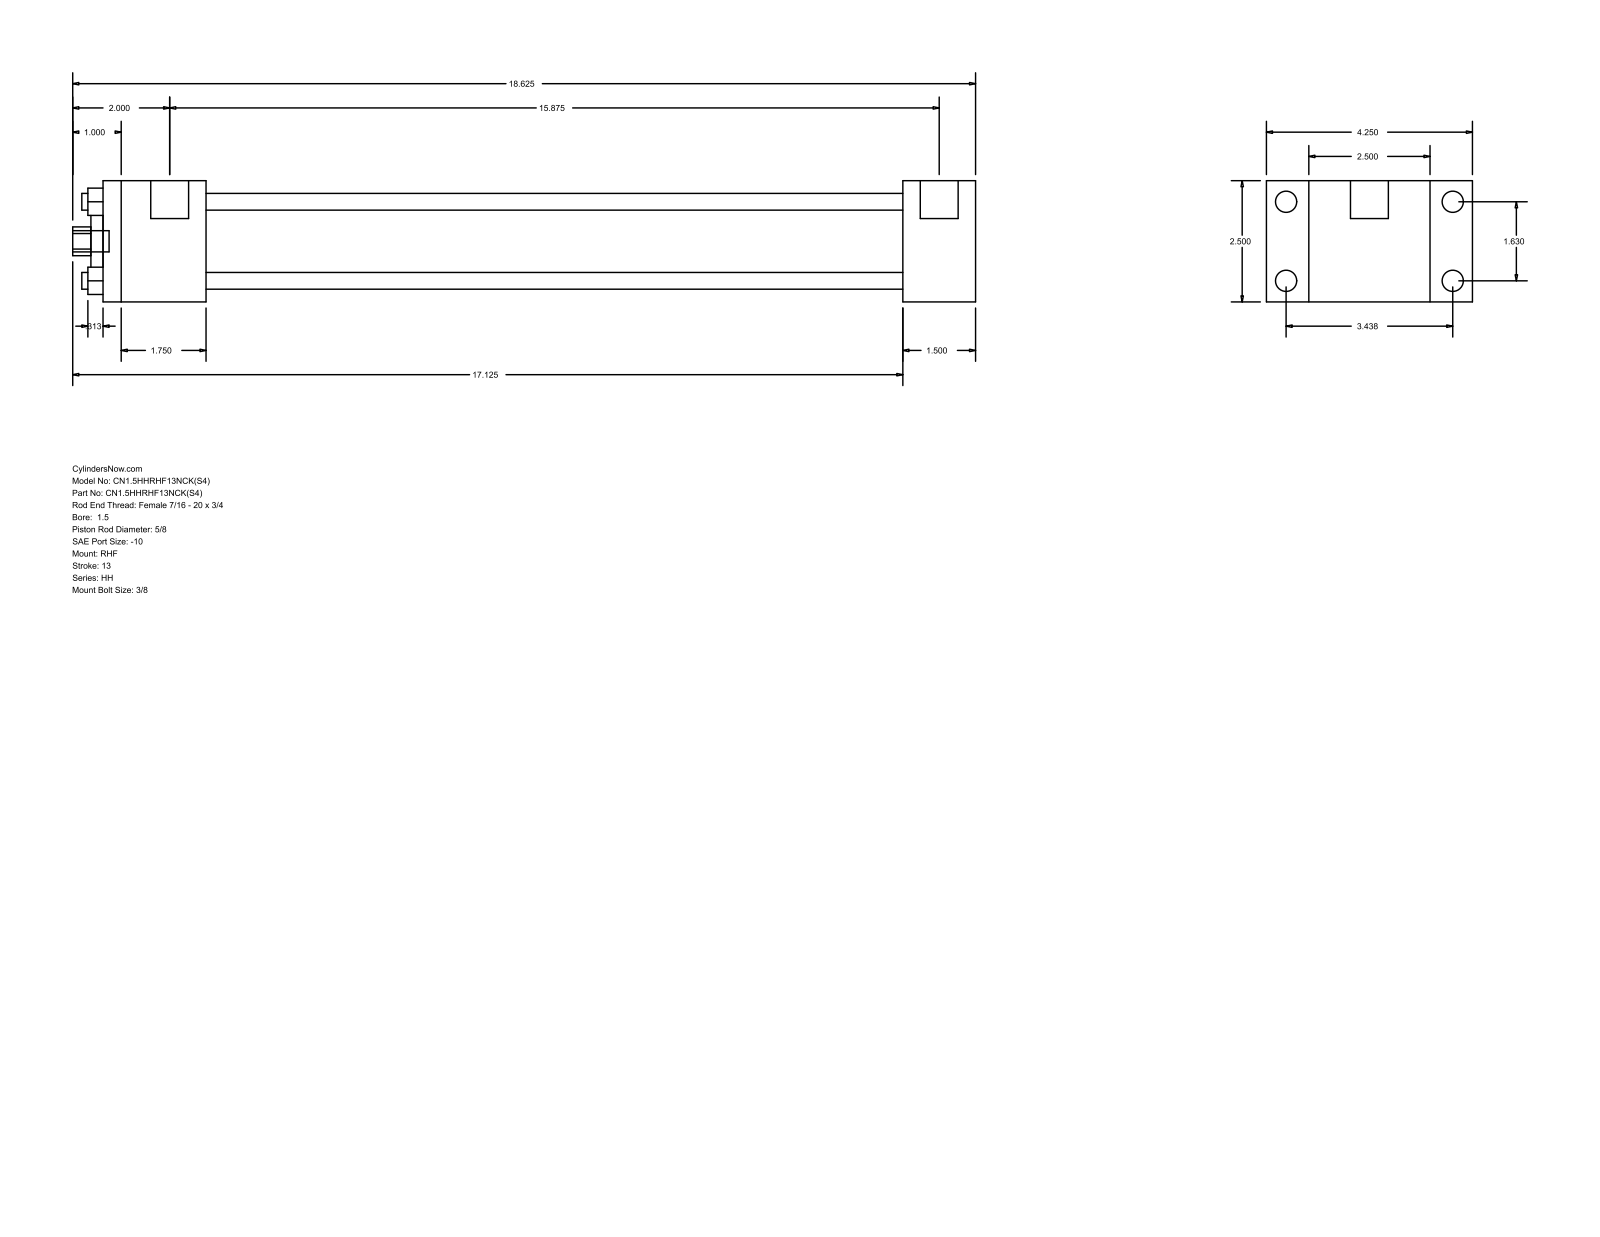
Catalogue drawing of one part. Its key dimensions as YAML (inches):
part_name: "HH_RHF__0150_0.625"
step_written_by: "GSSL Pune (CONFIG_CONTROL_DESIGN)"
units: inches
bodies: {solids: 0, faces: 88, planar: 60, cylindrical: 28, other: 0}
overall_size: [18.625, 4.25, 2.5]
round_holes:
  - {diameter: 0.345, count: 4}
  - {diameter: 0.625, count: 1}
  - {diameter: 1.125, count: 1}
  - {diameter: 1.75, count: 1}
round_bosses_or_shafts:
  - {diameter: 0.438, count: 4}
  - {diameter: 0.219, count: 4}
  - {diameter: 0.781, count: 2}
  - {diameter: 0.437, count: 1}
partial_cylinders:
  - {radius: 0.297, count: 1}
face_to_face_distances: [2.5, 0.875, 3.375, 1.5, 16.5, 18, 4.25, 2.125, 14.375, 15.875]
hole_center_spacings: [1.152, 1.63, 2.305]
